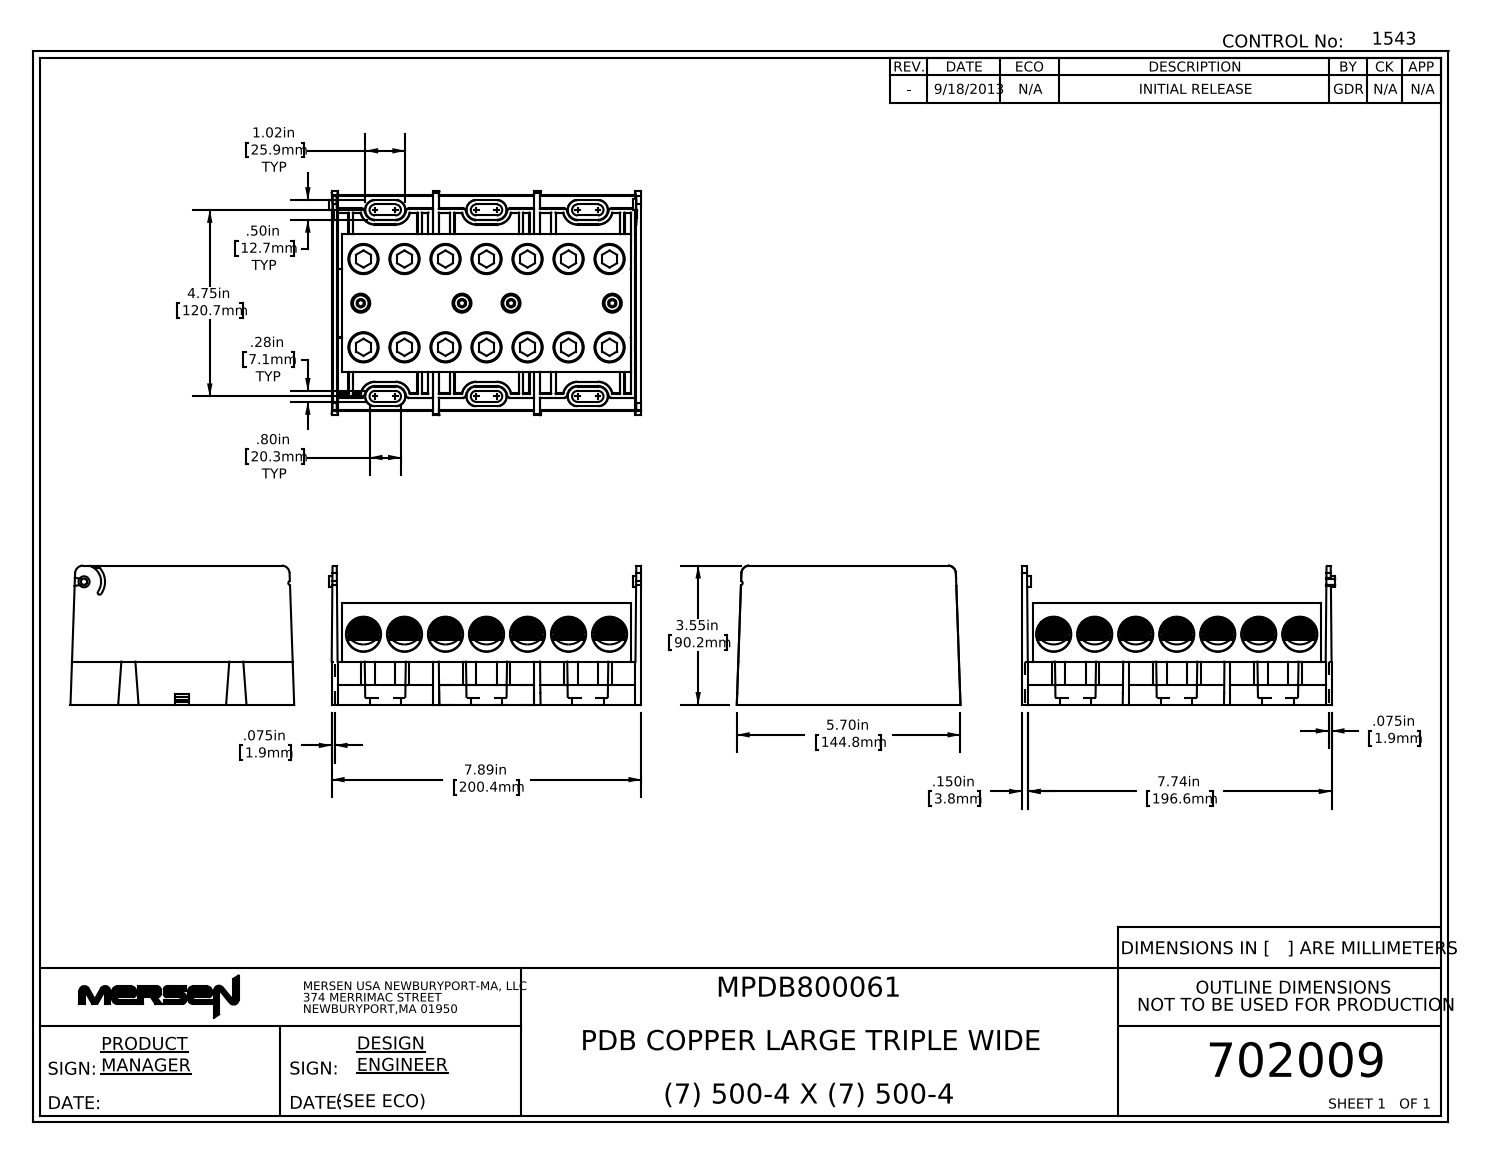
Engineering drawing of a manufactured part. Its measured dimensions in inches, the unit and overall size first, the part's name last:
Units: inches
Overall size (bounding box): 7.965 × 5.7 × 3.55
Round holes (diameter × count): ⌀0.75 ×14, ⌀0.875 ×7, ⌀0.484 ×4, ⌀0.16 ×1
Round bosses / shafts (diameter × count): ⌀0.28 ×2
Partial cylindrical surfaces — rounded edges, fillets, slot ends (radius × count): R0.035 ×42, R0.01 ×16, R0.141 ×12, R0.1 ×2, R0.2 ×2, R0.435 ×2, R0.535 ×2, R0.05 ×1
Main face-to-face distances: 2.58, 5.16, 7.74, 2.45, 0.85, 0.4, 1.5, 0.7, 1.1, 2.6
Hole centre spacings: 1.045, 2.09, 3.135, 2.48, 3.071, 3.859, 2.25, 1.045
Bodies: 0 solids, 954 faces (537 planar, 123 cylindrical, 294 other)
Part name (STEP PRODUCT): 420252
STEP written by: SolidWorks 2013 (AUTOMOTIVE_DESIGN)
